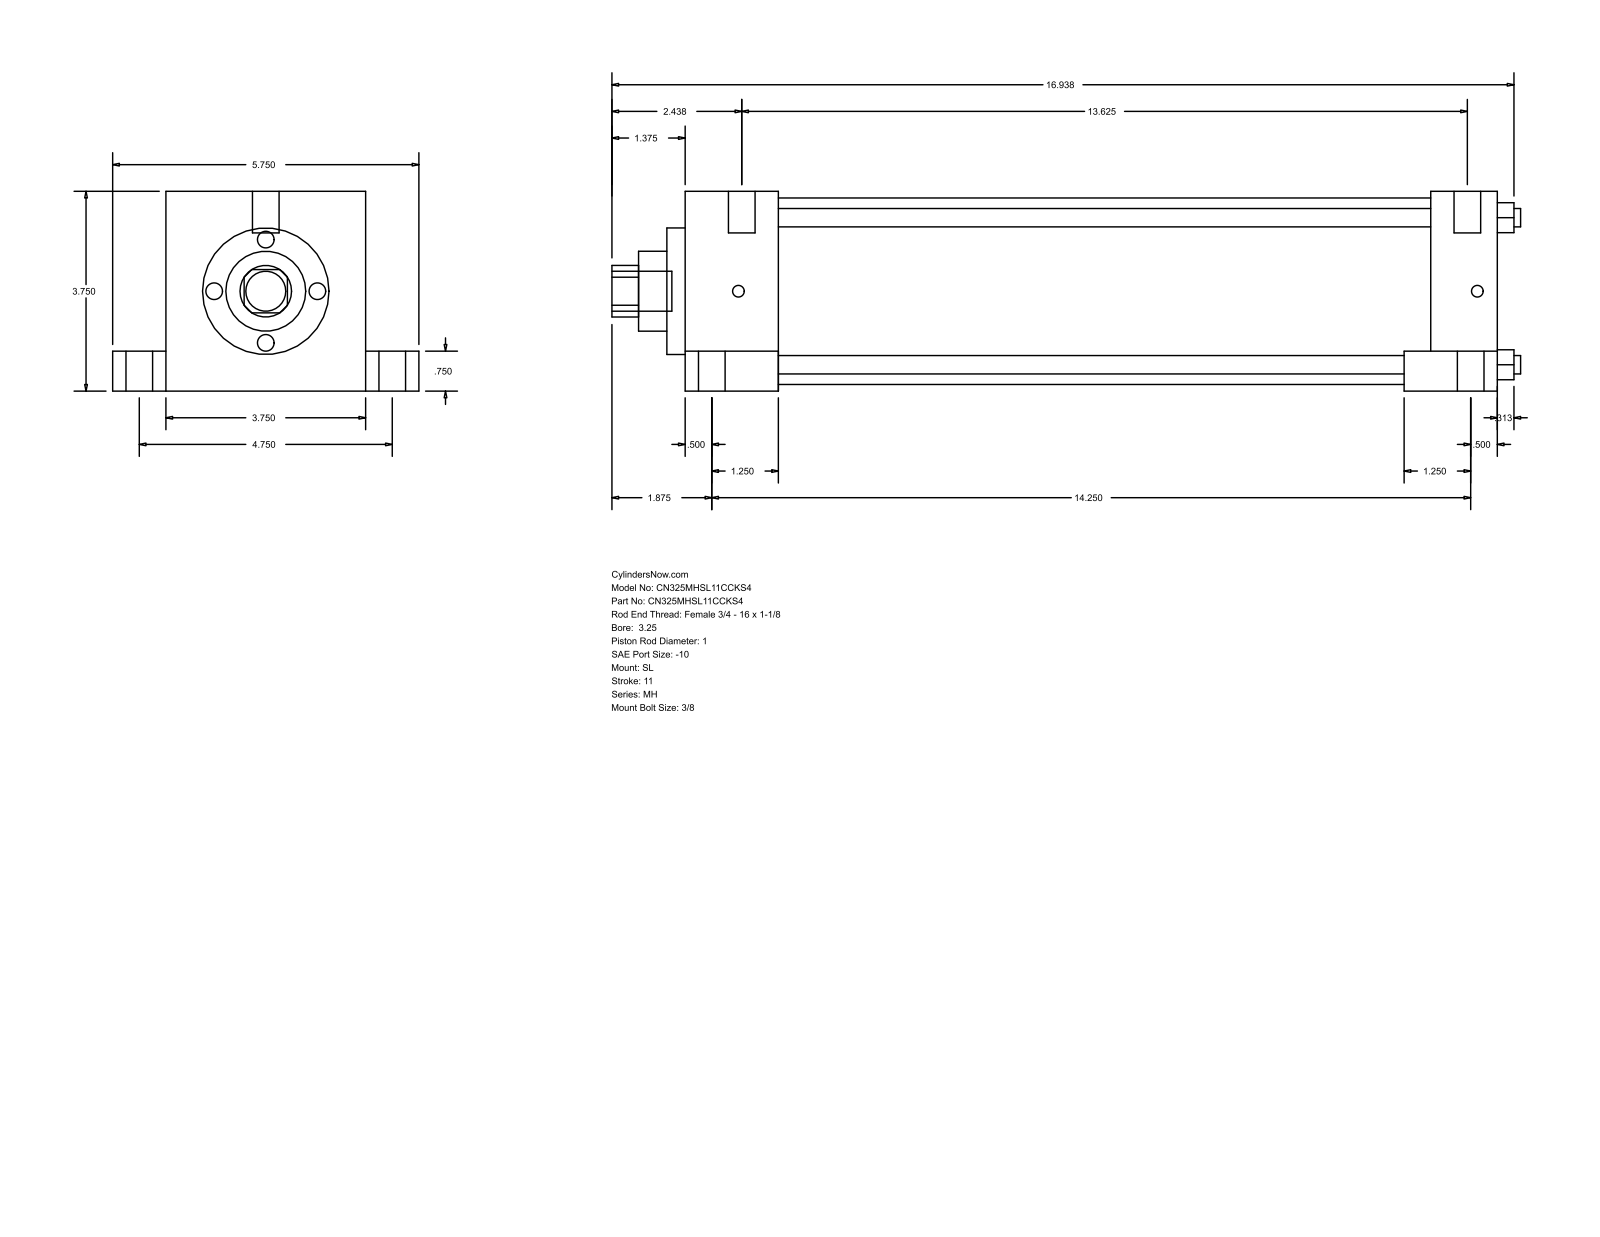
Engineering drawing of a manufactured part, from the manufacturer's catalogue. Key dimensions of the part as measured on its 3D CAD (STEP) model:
Part name (STEP PRODUCT): MH_SL__0325_1
STEP written by: GSSL Pune (CONFIG_CONTROL_DESIGN)
Units: millimetres
Bodies: 0 solids, 110 faces (77 planar, 33 cylindrical, 0 other)
Overall size (bounding box): 433.39 × 146.05 × 95.25
Round holes (diameter × count): ⌀8.76 ×4, ⌀25.4 ×1, ⌀38.1 ×1, ⌀60.33 ×1, ⌀88.9 ×1
Round bosses / shafts (diameter × count): ⌀12.7 ×6, ⌀19.05 ×5, ⌀5.56 ×4
Partial cylindrical surfaces — rounded edges, fillets, slot ends (radius × count): R12.29 ×1
Main face-to-face distances: 95.24, 387.35, 44.46, 342.89, 25.41, 120.65, 19.05, 76.19, 355.6, 311.14
Hole centre spacings: 49.57, 70.1, 99.14
